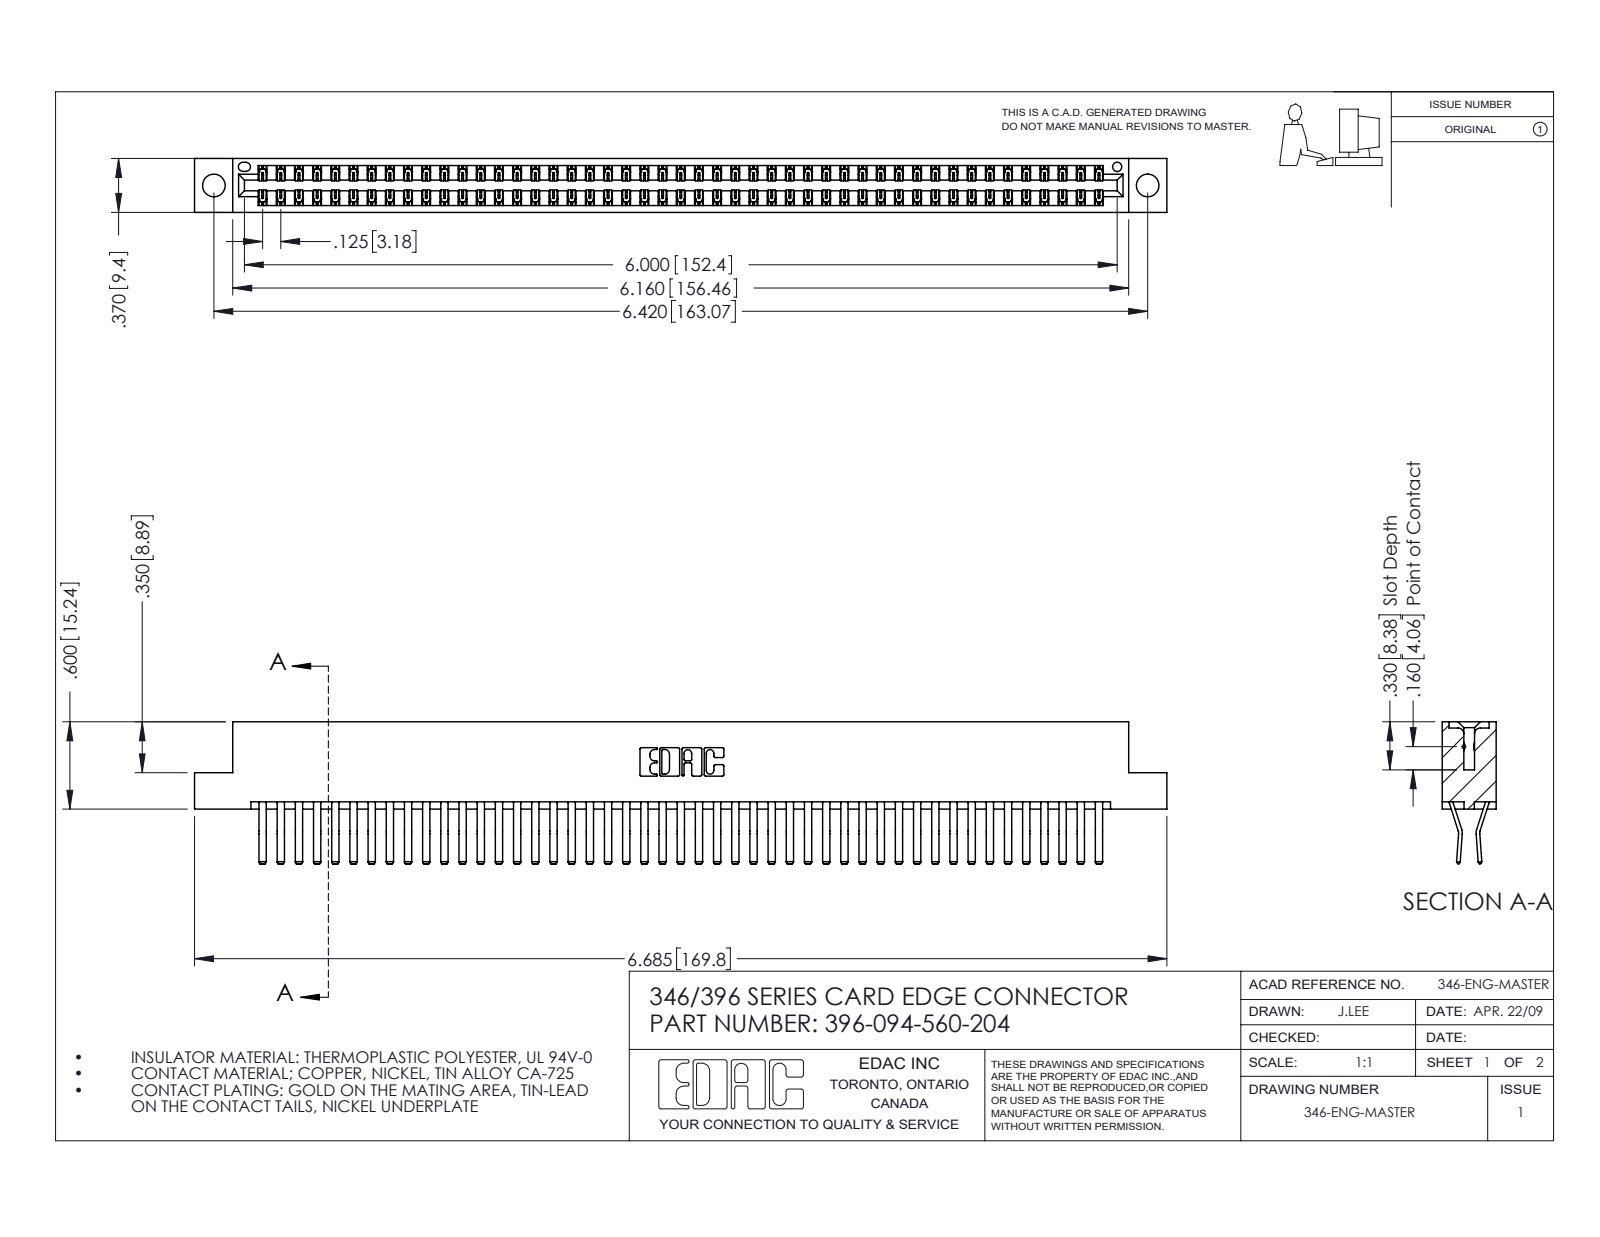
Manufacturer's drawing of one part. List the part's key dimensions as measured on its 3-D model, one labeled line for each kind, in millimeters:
Part name (STEP PRODUCT): 345-292-001_560 Tail; 396-094-560-204; 346 Part_Flush Mounting Lugs - 0.156 Dia-TH
STEP written by: SolidWorks 2016 (CONFIG_CONTROL_DESIGN)
Units: millimetres
Bodies: 95 solids, 5198 faces (3366 planar, 1832 cylindrical, 0 other)
Overall size (bounding box): 169.8 × 24.8 × 9.4
Volume: 17 120 mm³ · Surface area: 25 080 mm²
Round holes (diameter × count): ⌀4 ×2, ⌀1.6 ×1
Partial cylindrical surfaces — rounded edges, fillets, slot ends (radius × count): R0.2 ×141, R0.3 ×22, R0.2 ×6, R0.8 ×6, R0.7 ×3, R0.3 ×2, R0.4 ×2, R0.6 ×2
Main face-to-face distances: 1.2, 8.2, 9.4, 0.6, 6.4, 1.8, 7.6, 7, 3.8, 5.6
Hole centre spacings: 6.2, 157.8, 163.1
